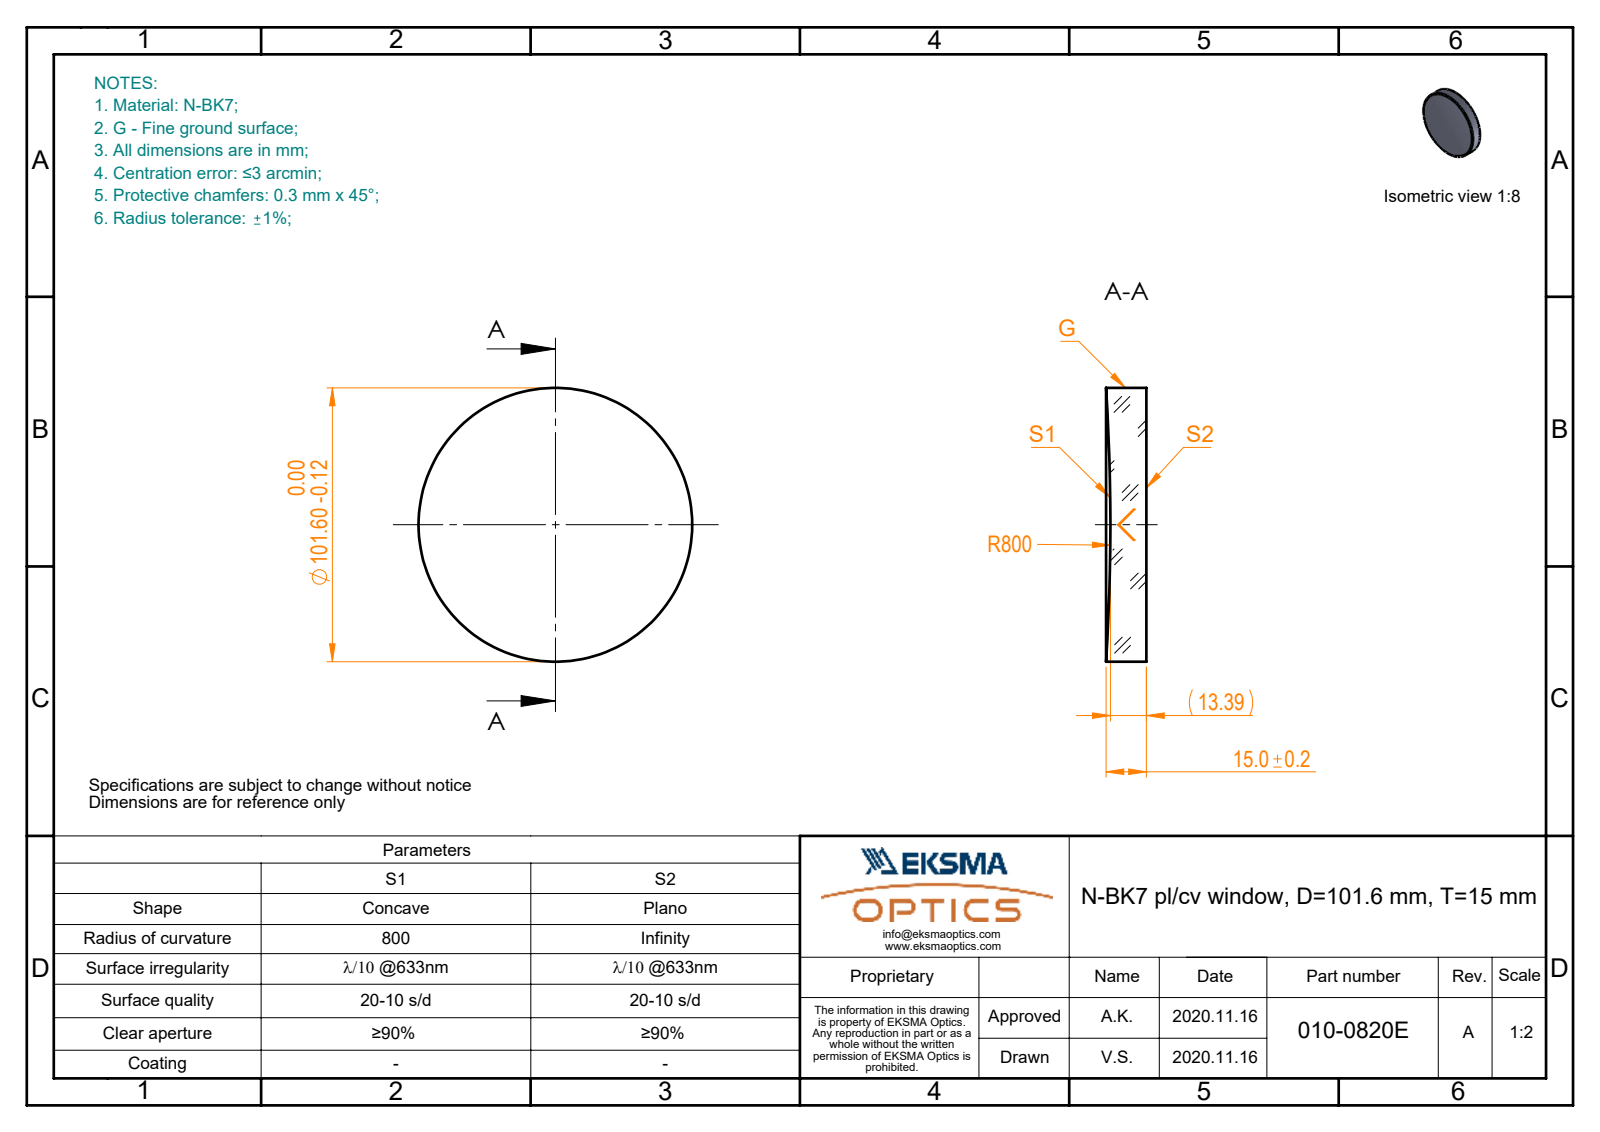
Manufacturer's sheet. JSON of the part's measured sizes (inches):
{"part_name": "010-0820E_N-BK7_PCV_window", "step_written_by": "SolidWorks 2019 (CONFIG_CONTROL_DESIGN)", "units": "inches", "bodies": {"solids": 1, "faces": 5, "planar": 1, "cylindrical": 2, "other": 2}, "overall_size": [4, 4, 0.591], "volume_in3": 7.022, "surface_area_in2": 32.57, "round_bosses_or_shafts": [[4, 1]]}
